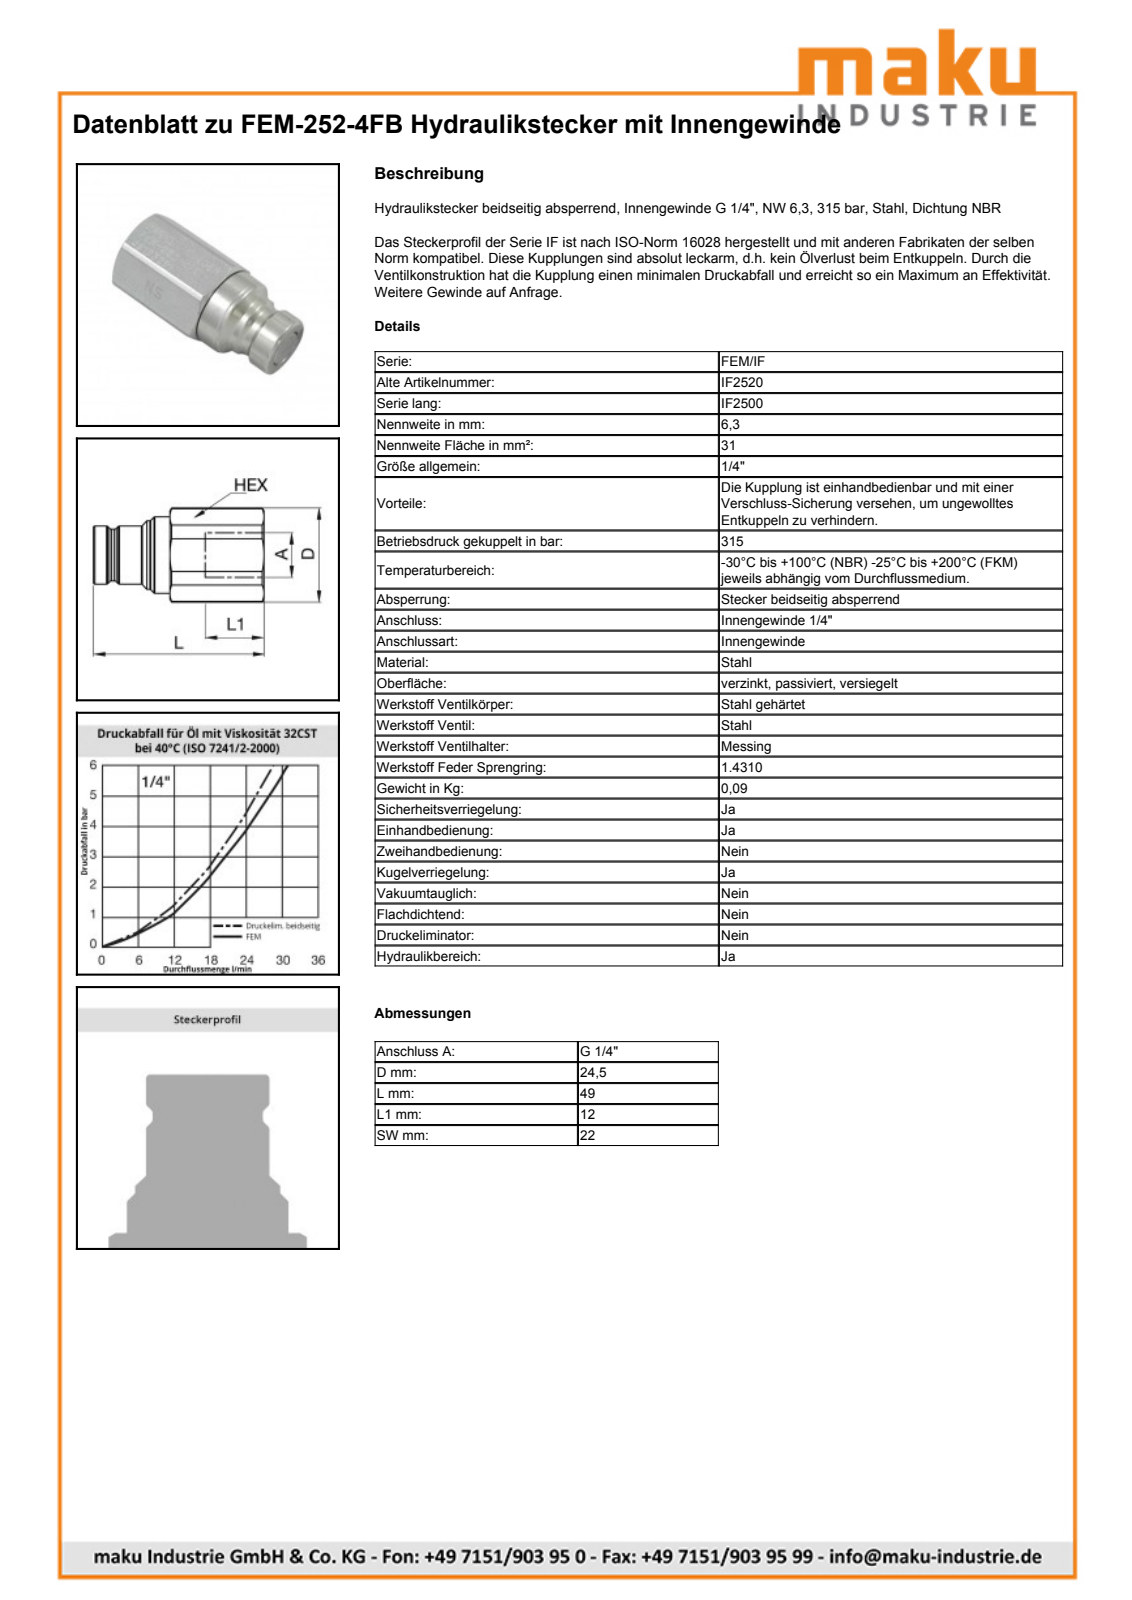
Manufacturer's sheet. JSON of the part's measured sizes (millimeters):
{"part_name": "FEM-252-4FB", "step_written_by": "SolidWorks 2009 (AUTOMOTIVE_DESIGN)", "units": "millimeters", "bodies": {"solids": 1, "faces": 79, "planar": 13, "cylindrical": 22, "other": 44}, "overall_size": [48.65, 24.5, 22], "volume_mm3": 15180, "surface_area_mm2": 4614, "round_holes": [[9.7, 1], [11.5, 1]], "round_bosses_or_shafts": [[21.1, 1], [20.75, 1], [19.86, 1], [16.15, 1], [13.95, 1]], "partial_cylinders_radius": [[12.25, 1]], "face_to_face_distances": [22, 15.43, 33.22, 48.65, 20.65, 12.57, 28, 20.57, 33.14, 48.57]}
